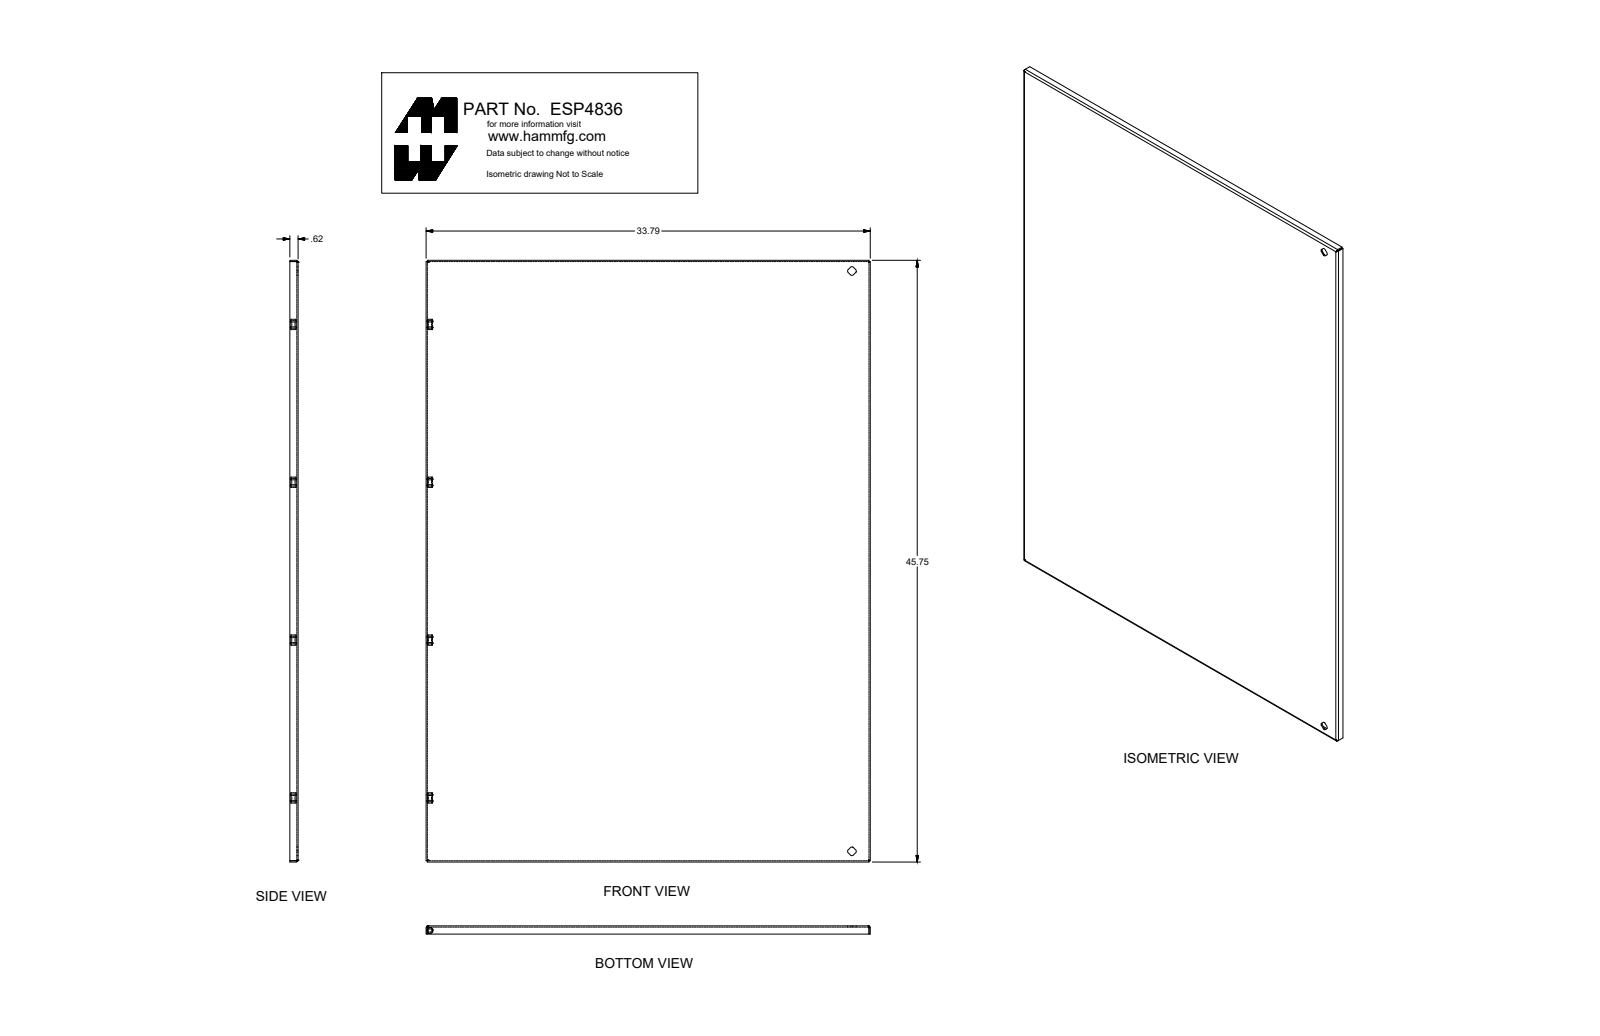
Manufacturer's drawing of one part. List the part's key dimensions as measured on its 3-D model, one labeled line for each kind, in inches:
Part name (STEP PRODUCT): ESP4836
STEP written by: SolidWorks 2018 (AUTOMOTIVE_DESIGN)
Units: inches
Bodies: 28 solids, 1012 faces (523 planar, 361 cylindrical, 128 other)
Overall size (bounding box): 45.75 × 35.856 × 6.757
Volume: 181 in³ · Surface area: 4 103 in²
Round holes (diameter × count): ⌀0.281 ×6, ⌀0.172 ×3, ⌀0.242 ×3, ⌀0.516 ×2, ⌀0.24 ×1, ⌀0.797 ×1
Round bosses / shafts (diameter × count): ⌀0.356 ×3, ⌀0.292 ×3, ⌀0.226 ×3, ⌀0.788 ×2, ⌀0.535 ×2, ⌀0.496 ×2, ⌀0.435 ×2, ⌀0.455 ×1
Partial cylindrical surfaces — rounded edges, fillets, slot ends (radius × count): R0.048 ×40, R0.01 ×36, R0.006 ×8, R0.063 ×8, R0.036 ×6, R0.108 ×6, R0.156 ×6, R0.06 ×4
Main face-to-face distances: 0.095, 0.072, 34.158, 0.748, 0.843, 0.82, 0.915, 34.23, 34.086, 22
Hole centre spacings: 22, 22.431, 4.375, 44, 44.217, 0.062, 44.098, 44.159
